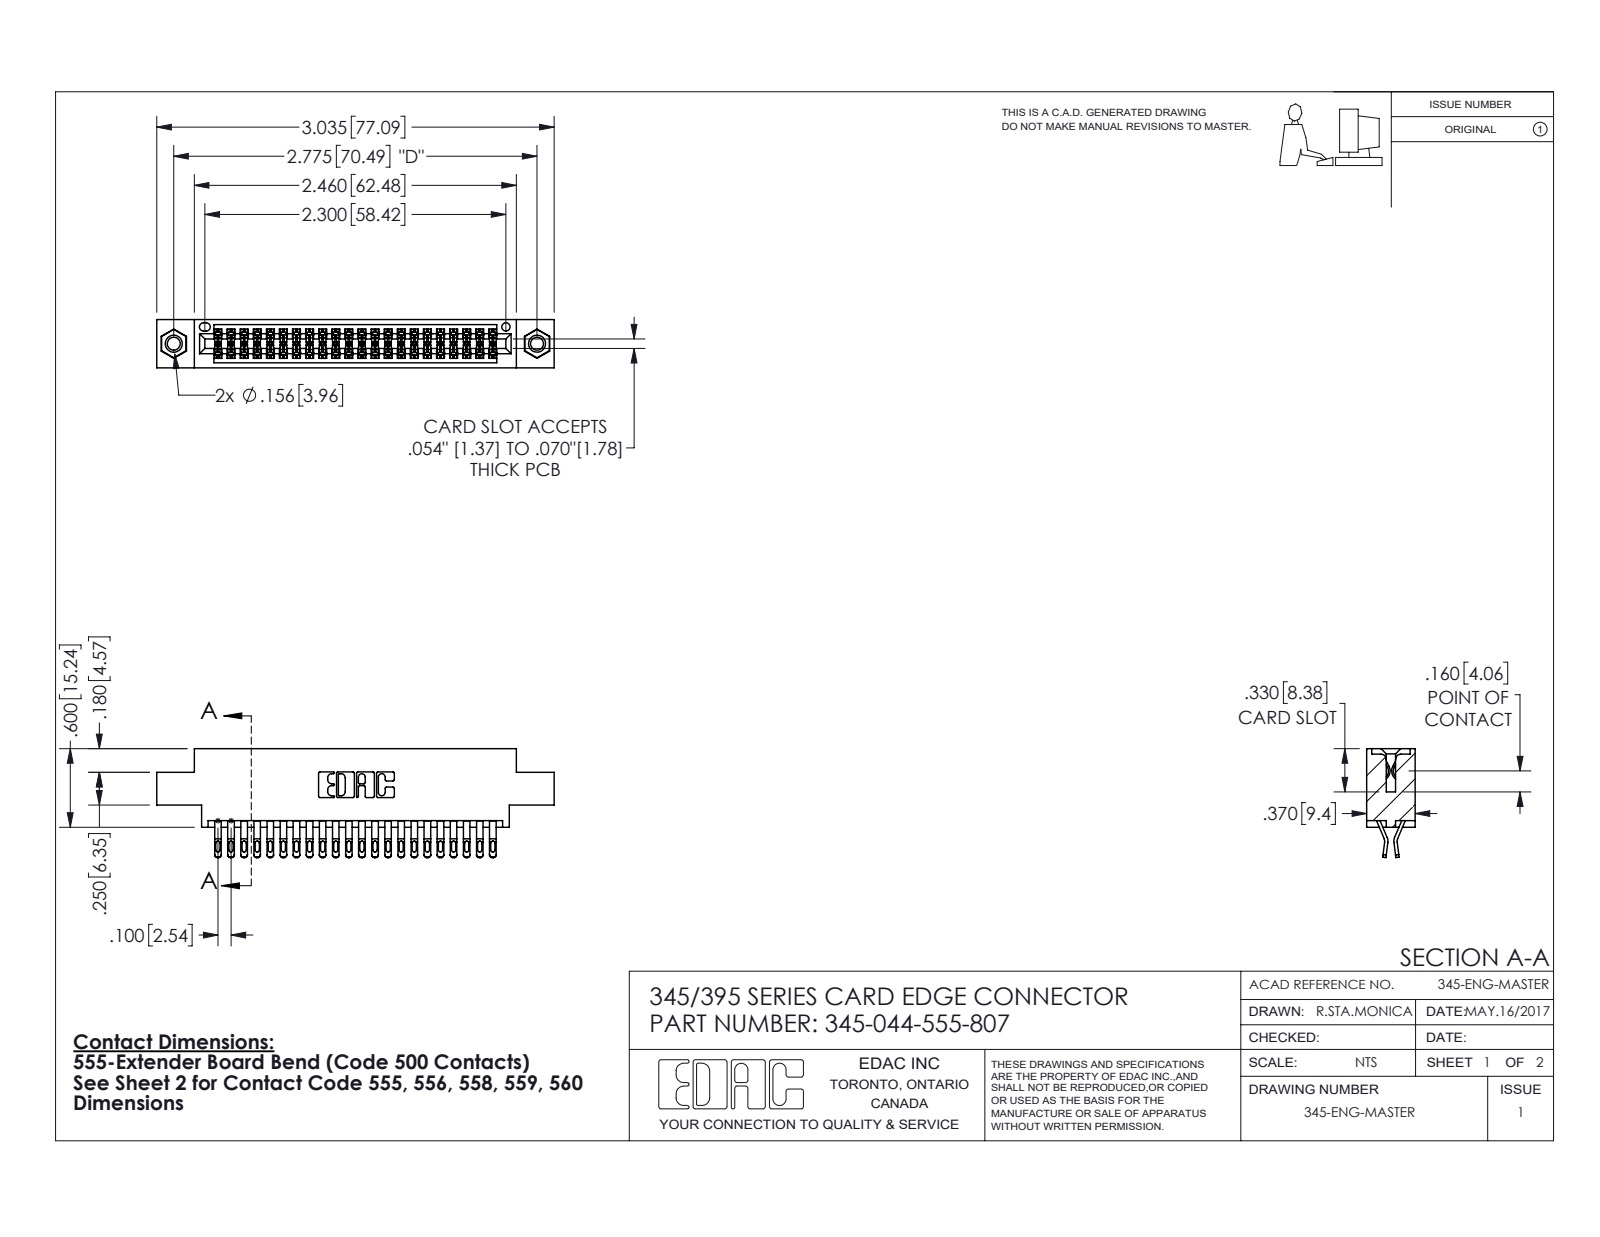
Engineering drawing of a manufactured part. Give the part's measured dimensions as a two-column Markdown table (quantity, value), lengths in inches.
| quantity | value |
| --- | --- |
| part name | 345-044-555-807; 345-250-001_345-250-005-103; 345-292-001_555 Tail; 345 Part_0.170 Offset - 0.156 Dia-TI |
| STEP written by | SolidWorks 2016 (CONFIG_CONTROL_DESIGN) |
| units | inches |
| bodies | 47 solids, 2654 faces (1480 planar, 1158 cylindrical, 16 other) |
| overall size | 3.035 × 0.832 × 0.37 |
| volume | 0.446 in³ |
| surface area | 17.09 in² |
| round holes (diameter × count) | 0.098 × 2, 0.125 × 2, 0.156 × 2, 0.064 × 1 |
| round bosses / shafts (diameter × count) | 0.155 × 2 |
| partial cylindrical surfaces (radius × count) | 0.016 × 110, 0.02 × 88, 0.006 × 66, 0.01 × 22, 0.007 × 6, 0.031 × 6, 0.026 × 3, 0.01 × 2 |
| main face-to-face distances | 0.072, 0.298, 0.37, 0.2, 0.025, 0.098, 0.272, 0.225, 0.175, 0.149 |
| hole center spacings | 0.27, 2.541, 2.775 |
